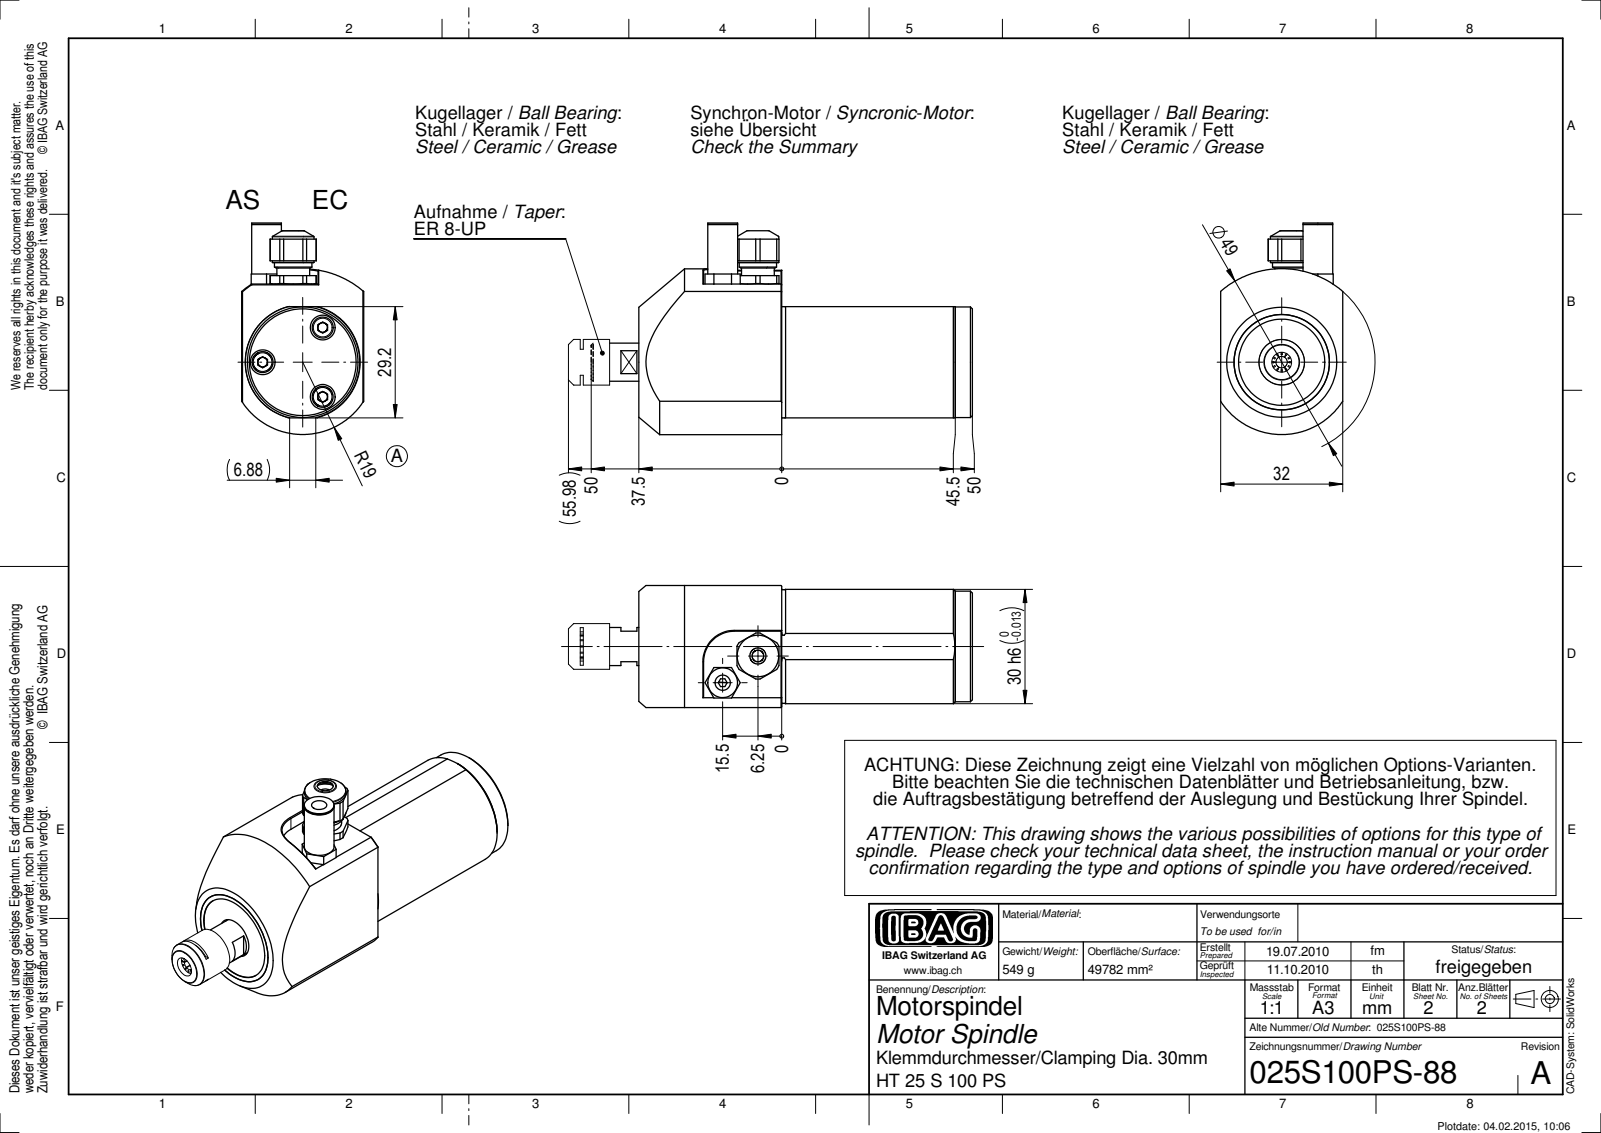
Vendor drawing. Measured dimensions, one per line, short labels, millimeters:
name: 025S100PS-88A
written by: SolidWorks 2010 (CONFIG_CONTROL_DESIGN)
unit: mm
bodies: 0 solids, 248 faces (115 planar, 78 cylindrical, 55 other)
size: 105.98 × 55.5 × 32
holes: 3× ⌀6.5, 2× ⌀3, 1× ⌀4, 1× ⌀4.2, 1× ⌀5.2, 1× ⌀9.15, 1× ⌀10.6, 1× ⌀22.6, 1× ⌀25
bosses: 2× ⌀5.5, 1× ⌀30, 1× ⌀29.8, 1× ⌀29, 1× ⌀12, 1× ⌀10.9, 1× ⌀10, 1× ⌀9.79
rounds: 1× R4.25, 1× R6.05, 1× R8, 1× R19, 1× R24.5
face distances: 32, 4.5, 45.5, 50, 37.4, 82.9, 87.4, 29.2, 5.9, 35.1
hole spacings: 10.5, 18.18, 11.6
